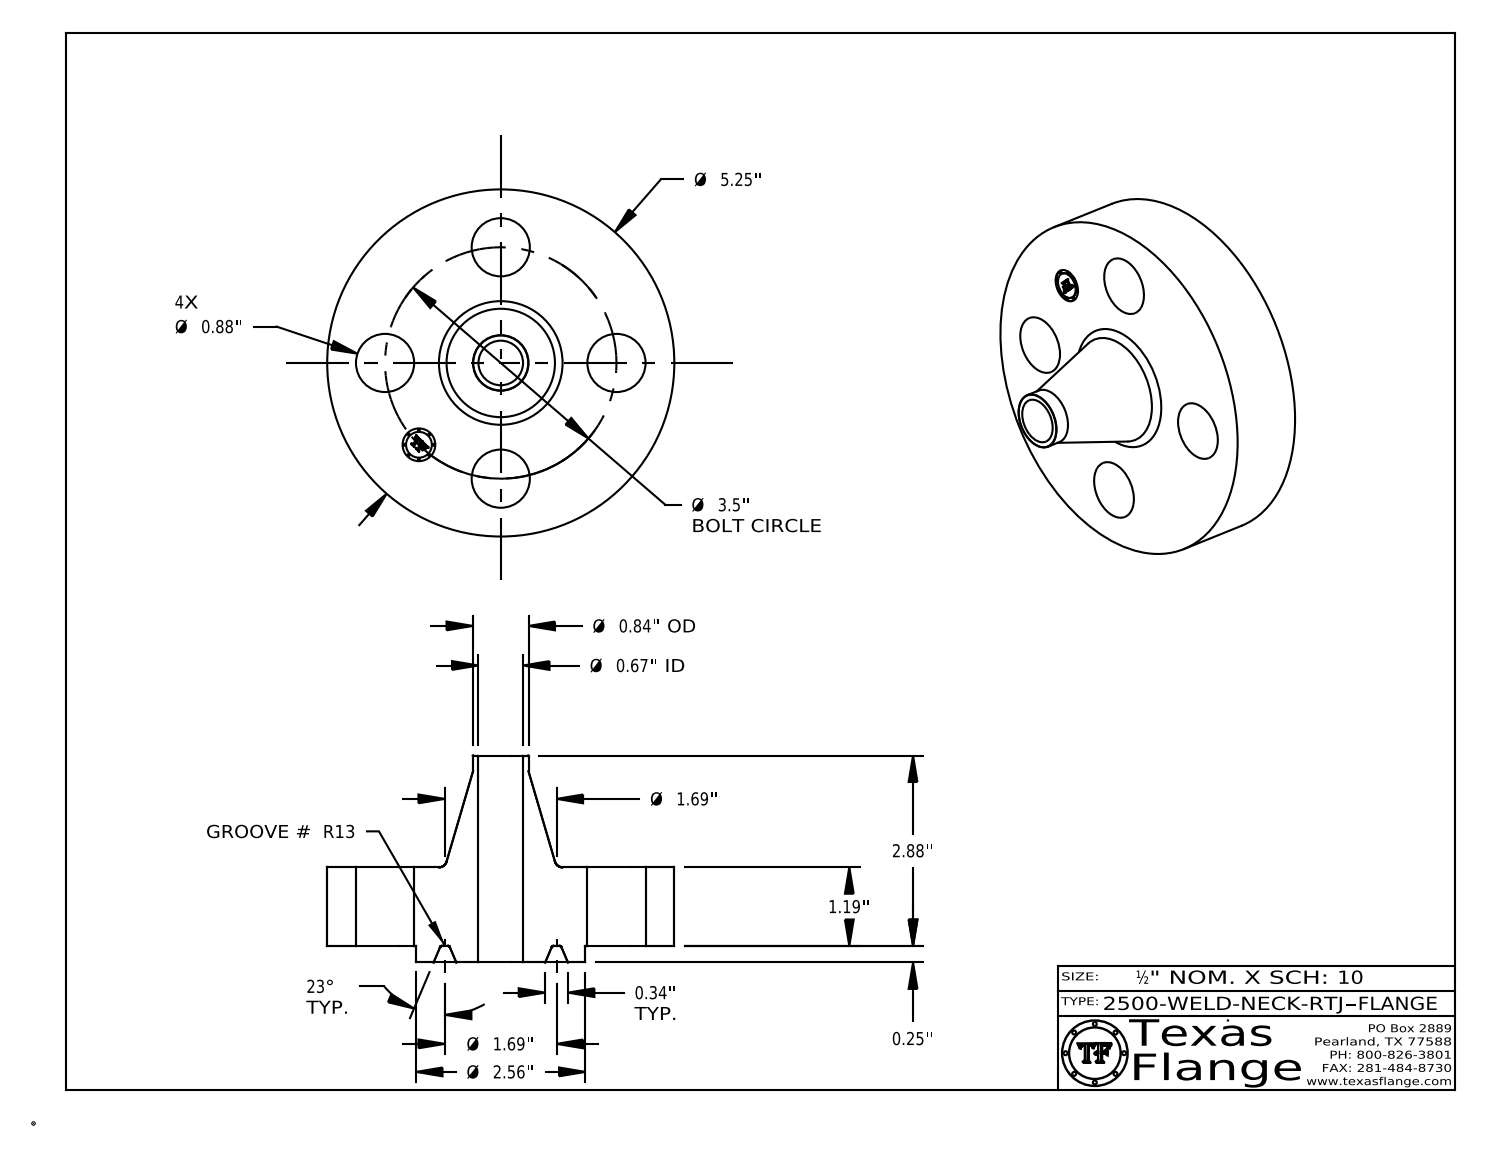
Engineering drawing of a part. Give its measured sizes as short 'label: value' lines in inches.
name: 2500-WELD-NECK-RTJ
written by: CATIA V5 STEP AP214 (AUTOMOTIVE_DESIGN)
unit: in
bodies: 1 solid, 421 faces (371 planar, 36 cylindrical, 14 other)
size: 5.25 × 5.25 × 3.13
volume: 24.76 in³; area: 85.75 in²
holes: 4× ⌀0.88, 1× ⌀0.495, 1× ⌀0.674
bosses: 8× ⌀0.03, 1× ⌀5.25, 1× ⌀2.563, 1× ⌀0.84, 1× ⌀0.39
face distances: 1.19, 0.25, 1.44, 3.13, 2.88, 1.69, 1.425, 1.175, 0.015, 1.705
hole spacings: 1.75, 2.475, 1.339, 3.233, 3.5
